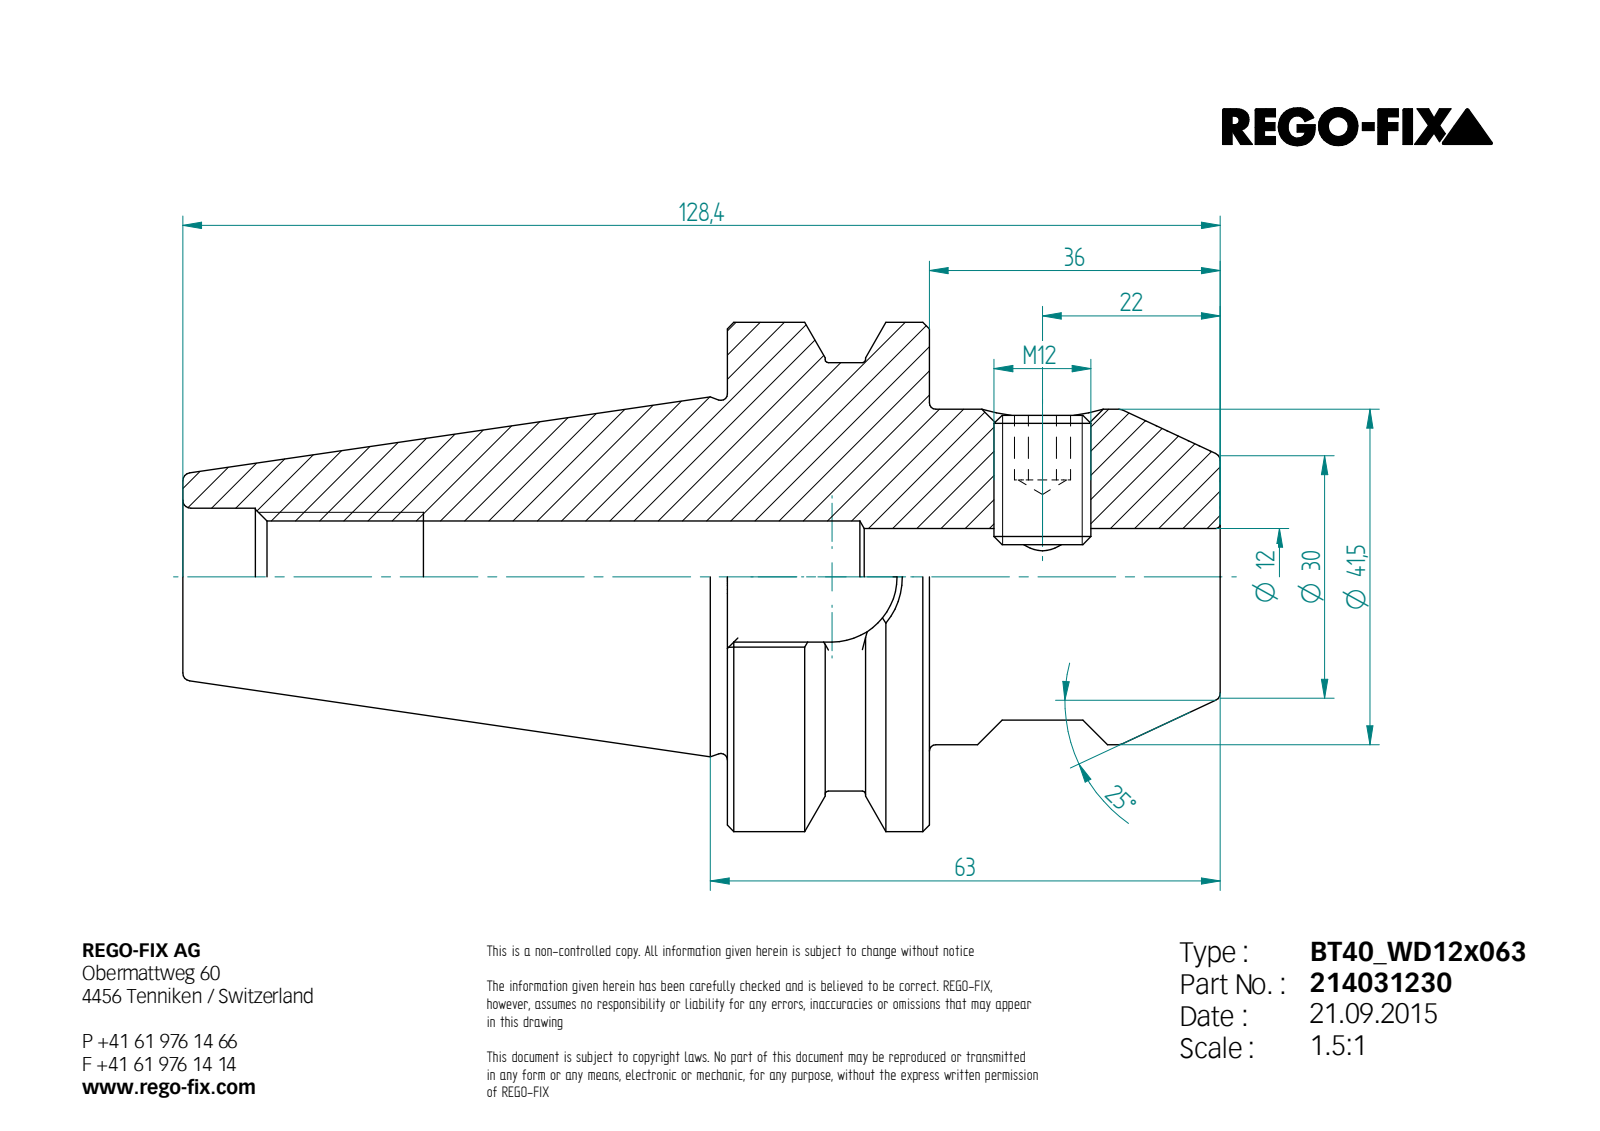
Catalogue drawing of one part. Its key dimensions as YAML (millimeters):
step_written_by: "Unknown (AUTOMOTIVE_DESIGN)"
units: millimeters
bodies: {solids: 2, faces: 102, planar: 53, cylindrical: 18, other: 31}
overall_size: [128.4, 63, 63]
volume: 160289
surface_area: 28805
round_holes:
  - {diameter: 10.11, count: 1}
  - {diameter: 12, count: 1}
  - {diameter: 13.84, count: 1}
  - {diameter: 17, count: 1}
round_bosses_or_shafts:
  - {diameter: 63, count: 1}
  - {diameter: 53, count: 1}
  - {diameter: 41.5, count: 1}
  - {diameter: 12, count: 1}
partial_cylinders:
  - {radius: 0.5, count: 4}
  - {radius: 8.05, count: 1}
face_to_face_distances: [25, 61, 36, 45.1, 67.4, 92.4, 128.4, 9.65, 25.75, 16.1]
